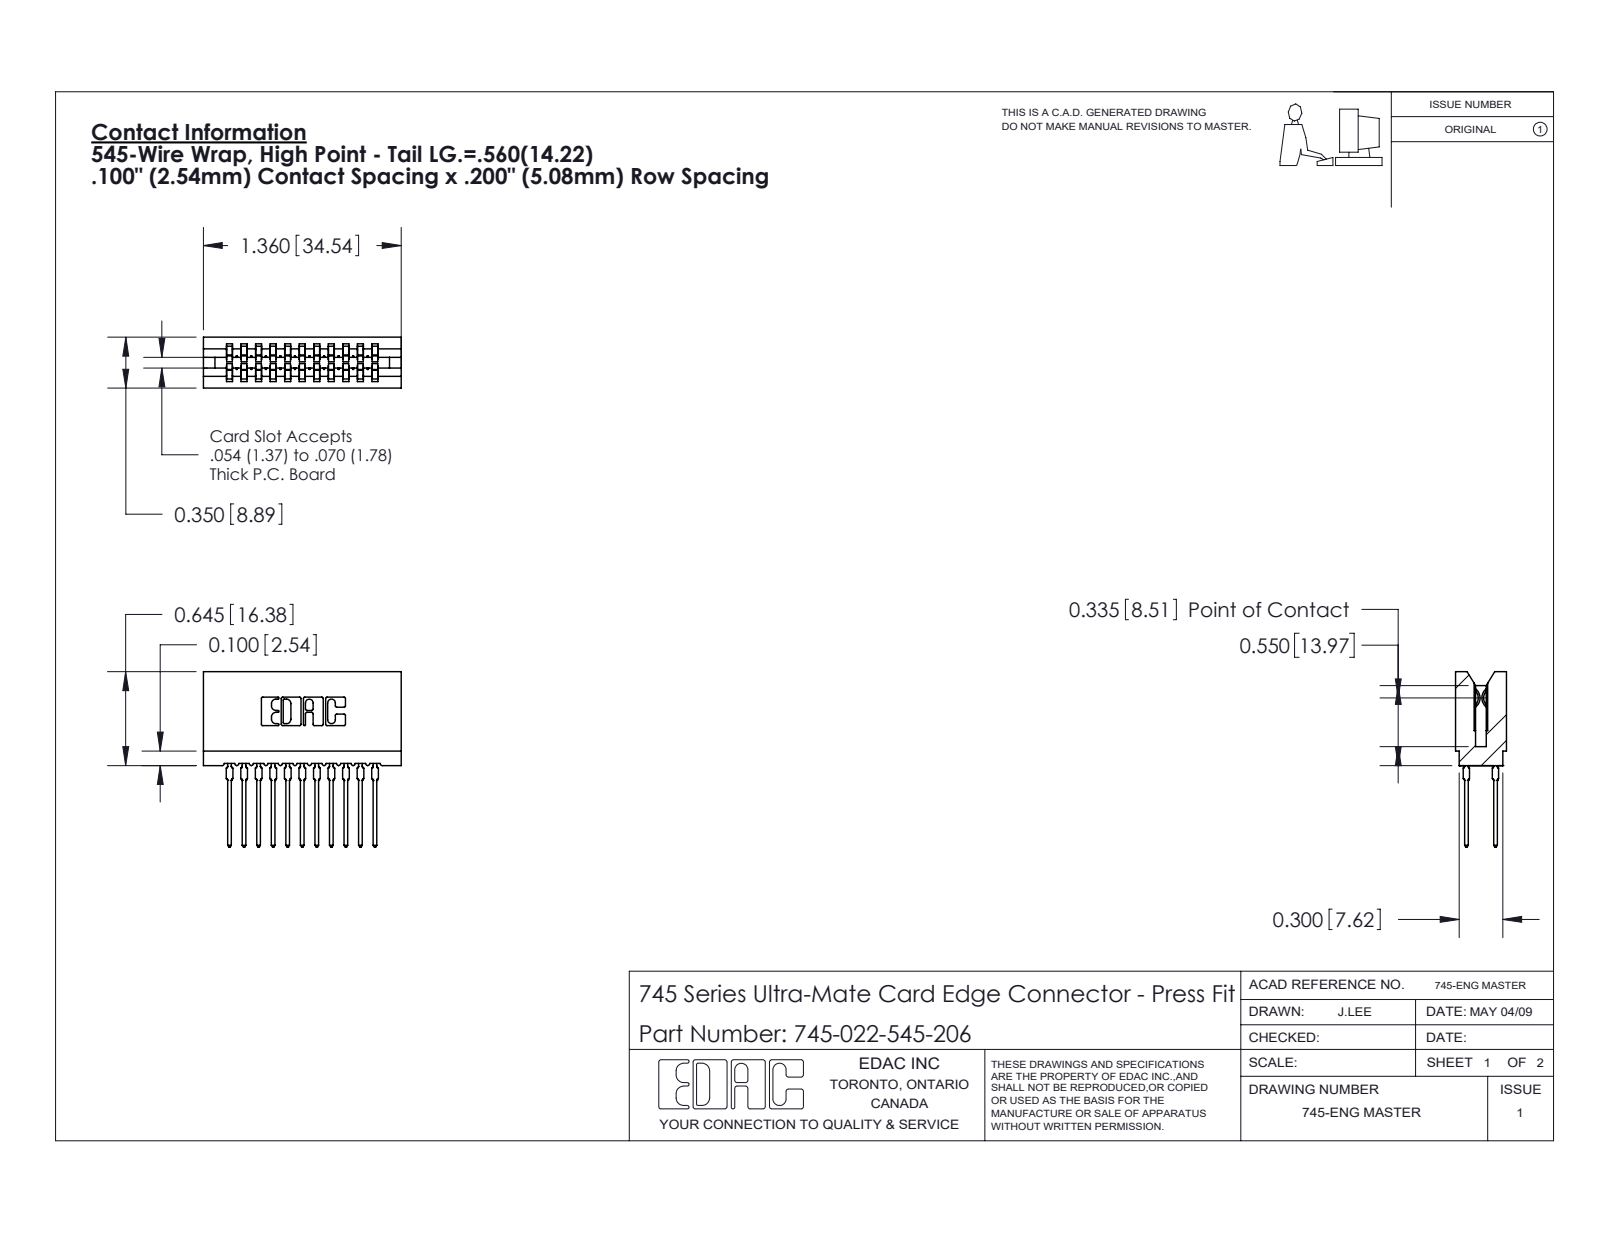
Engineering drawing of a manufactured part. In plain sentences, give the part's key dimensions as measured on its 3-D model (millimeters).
The part is named "745-292-001_545; 745-022-545-206; 745 Part_Insulator Option - 06". Its 3-D file was written by "SolidWorks 2020 (CONFIG_CONTROL_DESIGN)". It is 23 solids with 2065 faces: 1068 planar, 425 cylindrical and 572 other. Overall it measures 34.5 by 30.6 by 8.9 millimeters. Its volume is 3 360 cubic millimeters and its surface area 6 465 square millimeters. Partial cylindrical surfaces (rounded edges, fillets, slot ends): 44 of radius 0.5, 22 of radius 0.3, 22 of radius 0.4, 8 of radius 0.1, 8 of radius 0.3, 6 of radius 0.2, 6 of radius 0.8, 3 of radius 0.7. The main face-to-face distances are 5.1, 2.5, 7.6, 10.2, 12.7, 1.5, 3.6, 6.6, 1.1, 4.
